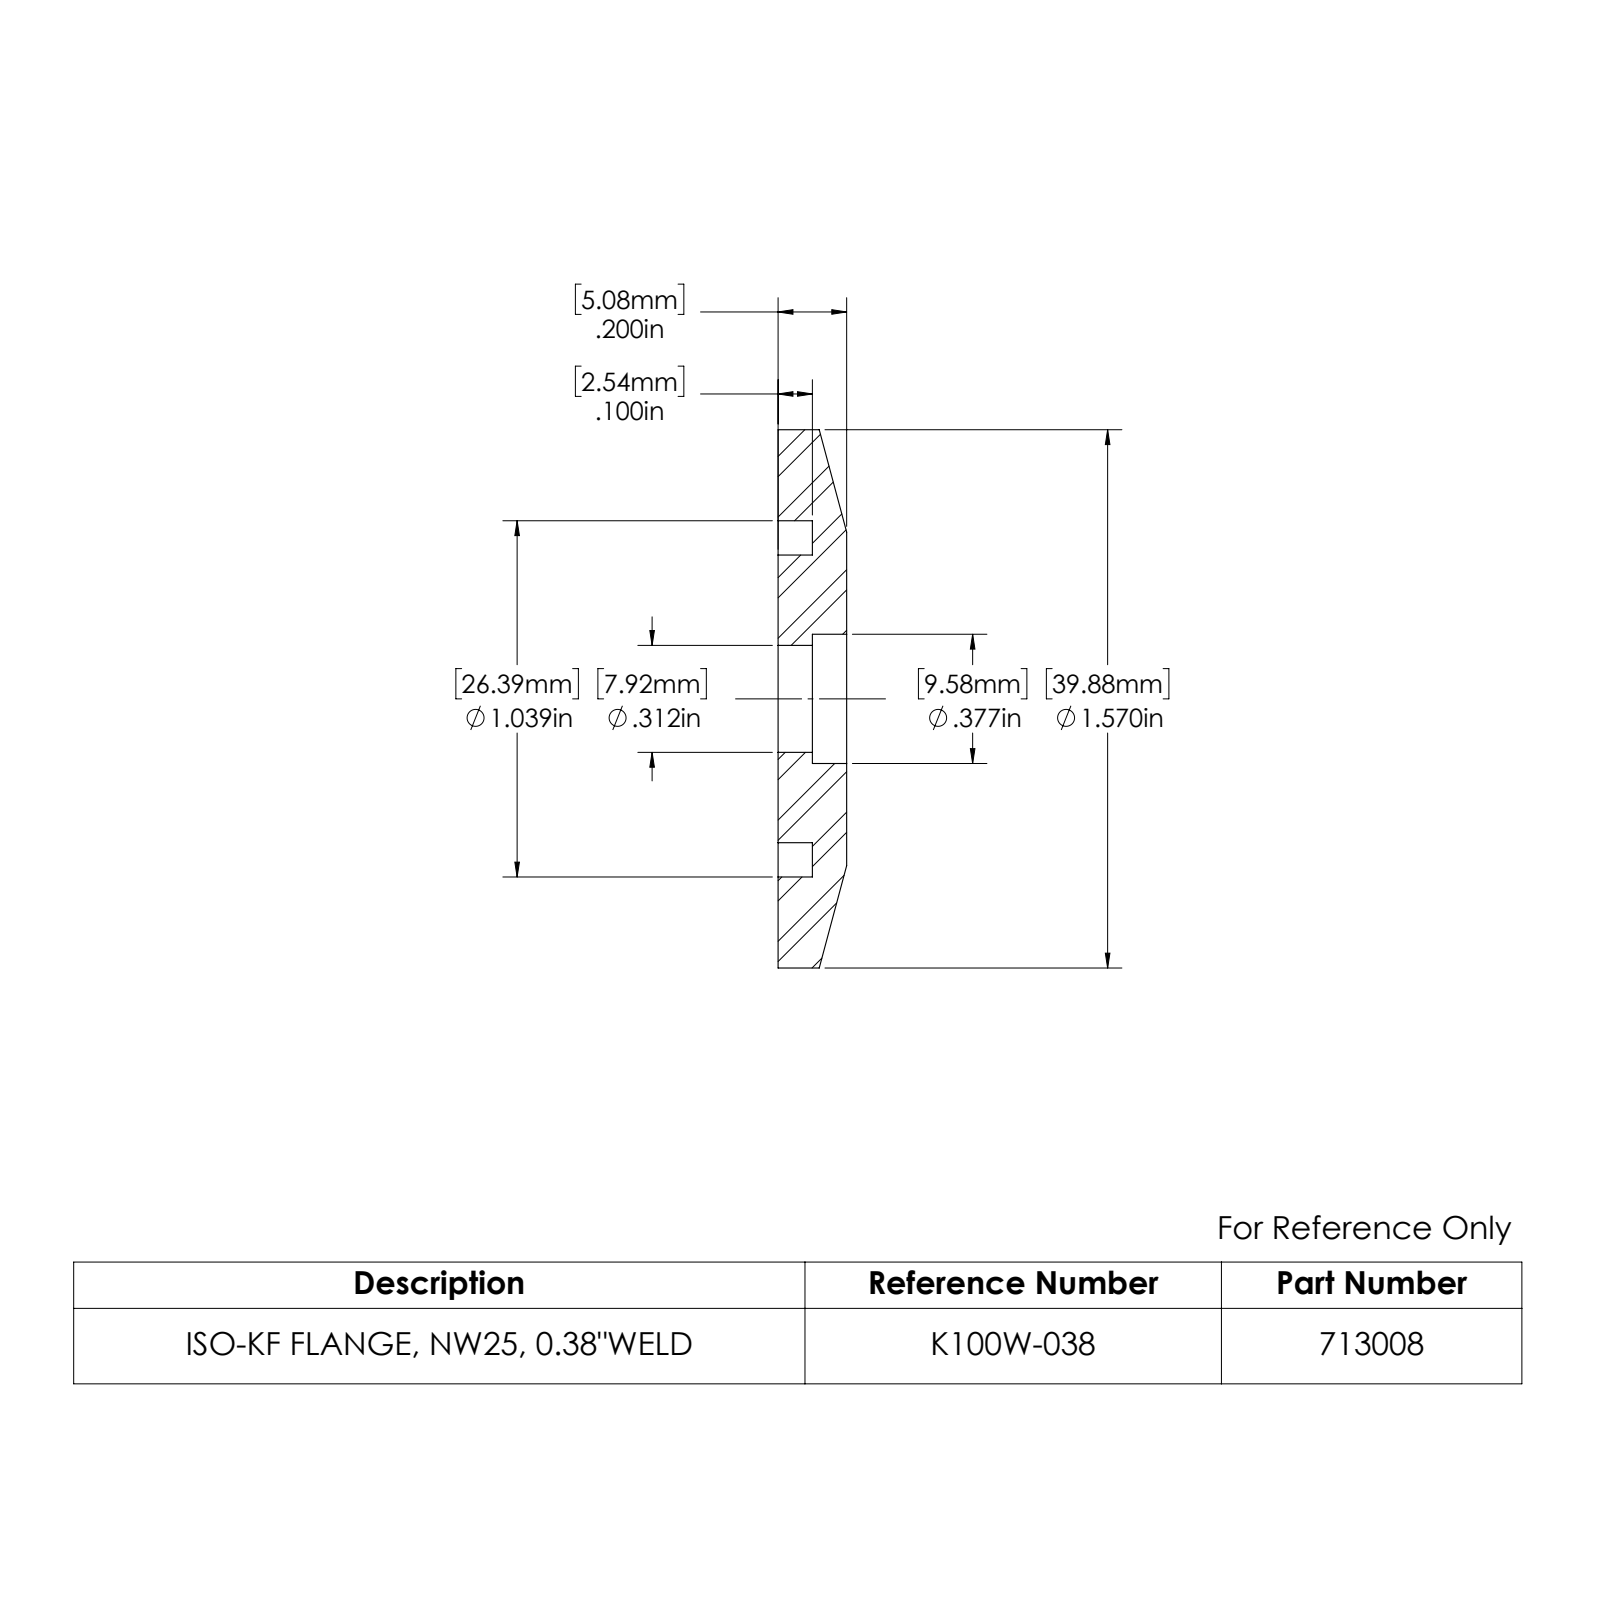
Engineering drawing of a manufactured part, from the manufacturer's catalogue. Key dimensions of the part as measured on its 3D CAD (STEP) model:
Part name (STEP PRODUCT): 713008
STEP written by: SolidWorks 2022 (AUTOMOTIVE_DESIGN)
Units: inches
Bodies: 1 solid, 17 faces (5 planar, 10 cylindrical, 2 other)
Overall size (bounding box): 1.57 × 1.57 × 0.2
Volume: 0.287 in³ · Surface area: 5.159 in²
Round holes (diameter × count): ⌀0.312 ×1, ⌀0.377 ×1, ⌀1.039 ×1
Round bosses / shafts (diameter × count): ⌀1.57 ×1, ⌀0.839 ×1
Main face-to-face distances: 0.1, 0.2
